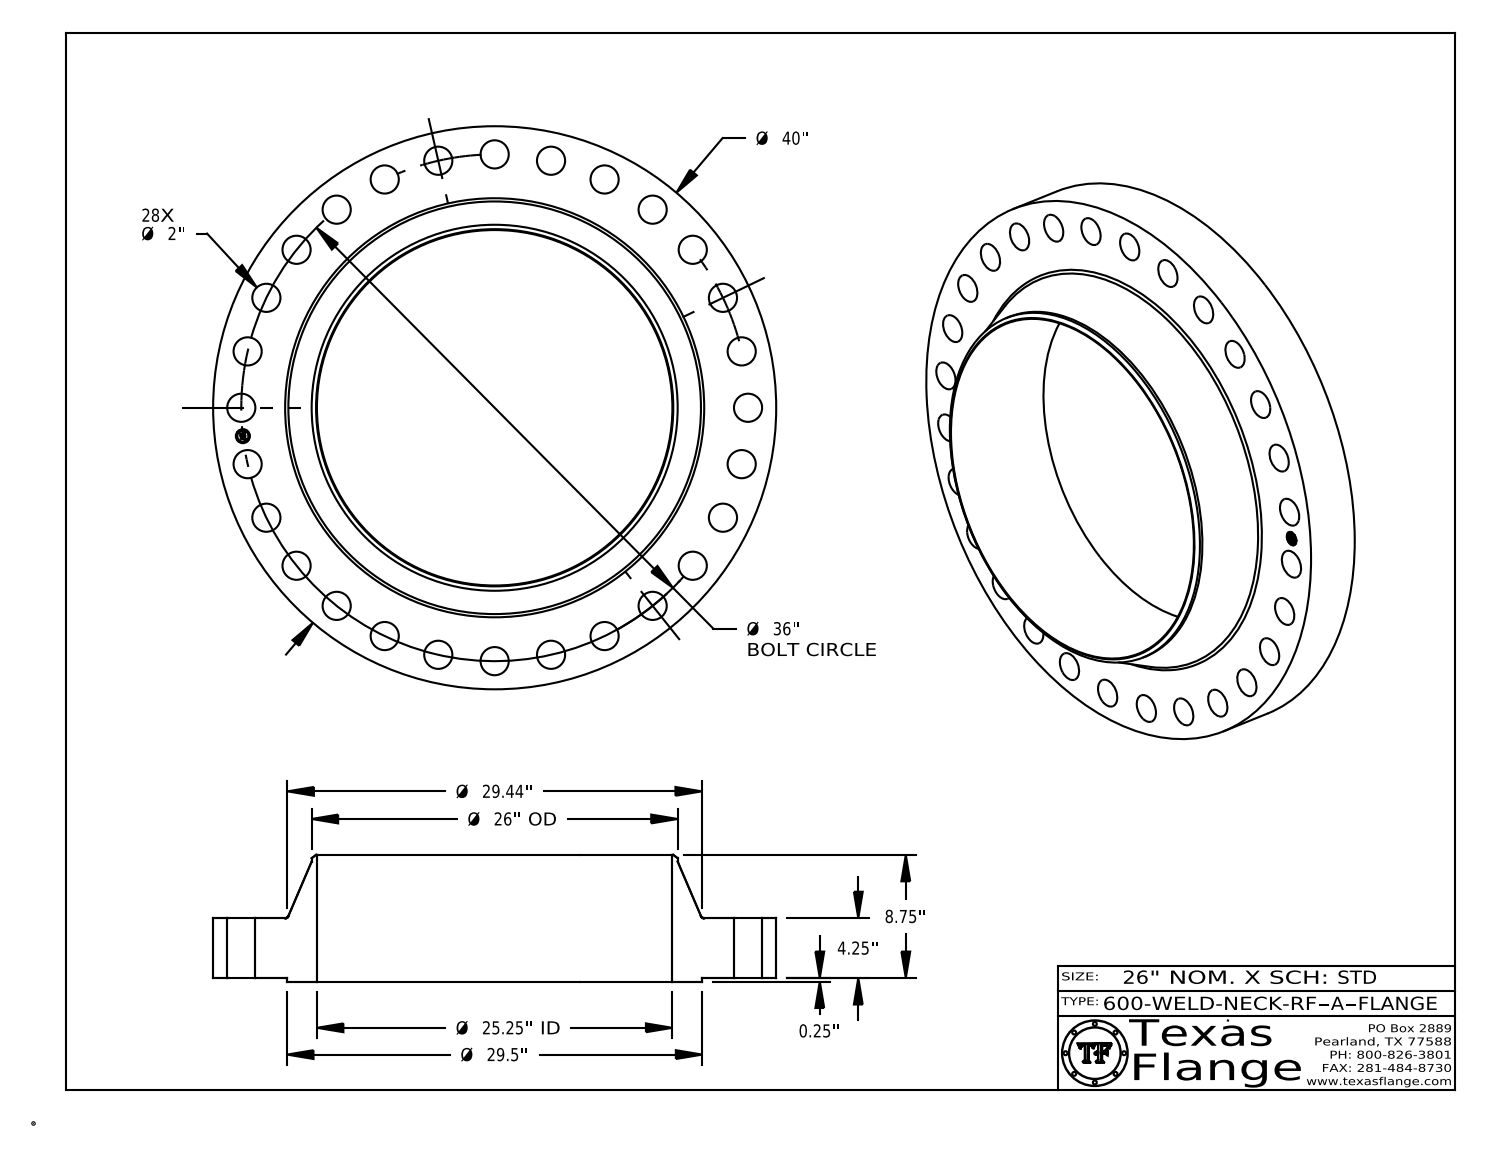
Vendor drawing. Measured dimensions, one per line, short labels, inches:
name: 600-WELD-NECK-RF, Series A
written by: CATIA V5 STEP AP214 (AUTOMOTIVE_DESIGN)
unit: in
bodies: 1 solid, 459 faces (369 planar, 84 cylindrical, 6 other)
size: 40 × 40 × 9
volume: 3 313 in³; area: 3 609 in²
holes: 28× ⌀2, 1× ⌀1, 1× ⌀25.25
bosses: 8× ⌀0.061, 1× ⌀40, 1× ⌀29.5, 1× ⌀26, 1× ⌀0.788
face distances: 4.25, 4.5, 0.25, 9, 8.75, 0.015, 4.485, 4.235, 4.515, 0.298
hole spacings: 18, 19.153, 4.031, 8.011, 11.89, 15.62, 22.446, 25.456
